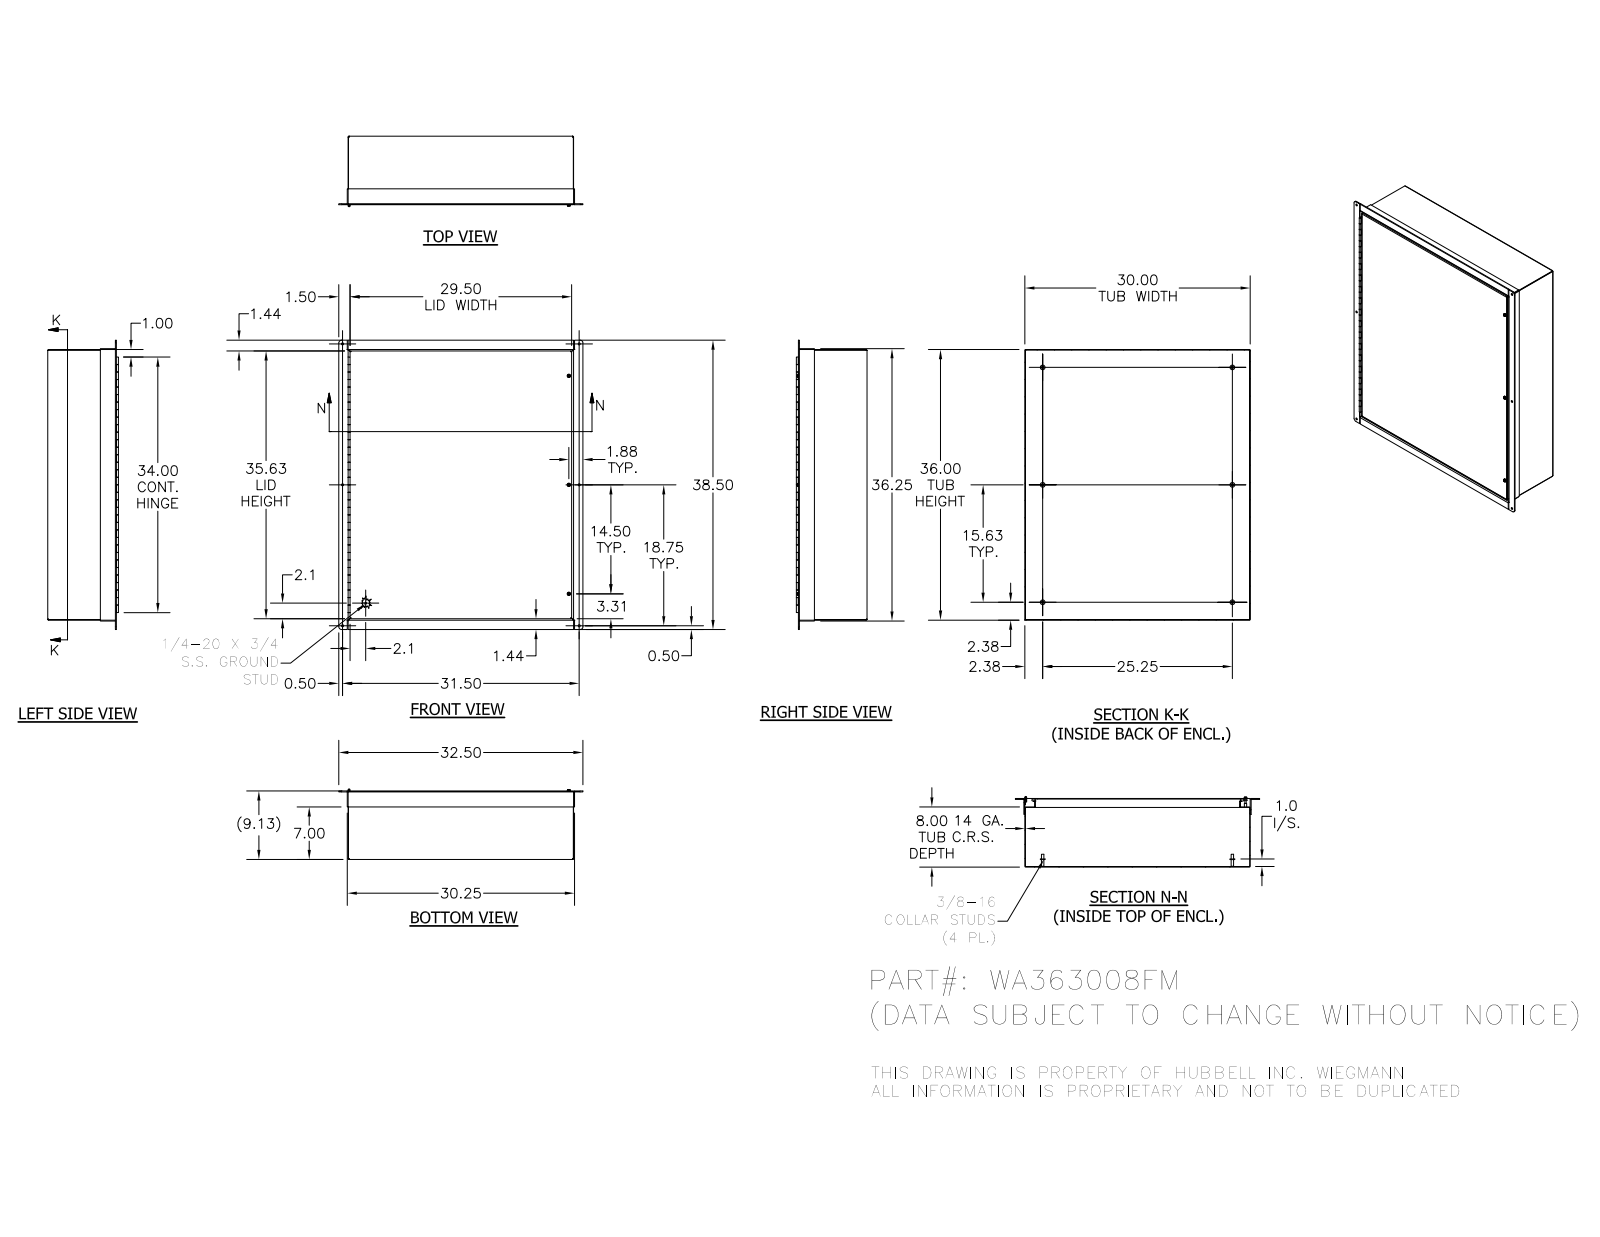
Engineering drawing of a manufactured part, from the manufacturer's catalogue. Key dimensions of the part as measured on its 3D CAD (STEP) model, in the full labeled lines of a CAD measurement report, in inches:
Part name (STEP PRODUCT): WA363008FMBKP; WA3630FMLID; 388116; H6010103T (+8 more)
STEP written by: Autodesk Inventor 2016 (AUTOMOTIVE_DESIGN)
Units: inches
Bodies: 29 solids, 804 faces (508 planar, 215 cylindrical, 81 other)
Overall size (bounding box): 38.5 × 32.5 × 9.4
Volume: 334.4 in³ · Surface area: 8 320 in²
Round holes (diameter × count): ⌀0.281 ×9, ⌀0.375 ×6, ⌀0.156 ×3, ⌀0.188 ×3, ⌀0.278 ×3, ⌀0.125 ×1
Round bosses / shafts (diameter × count): ⌀0.625 ×6, ⌀0.33 ×6, ⌀0.453 ×3, ⌀0.437 ×3, ⌀0.414 ×3, ⌀0.313 ×3, ⌀0.19 ×3, ⌀0.031 ×3
Partial cylindrical surfaces — rounded edges, fillets, slot ends (radius × count): R0.031 ×24, R0.105 ×20, R0.07 ×8, R0.125 ×8, R0.156 ×4, R0.375 ×4, R0.089 ×3
Main face-to-face distances: 0.074, 9.041, 8.967, 9.115, 29.926, 35.926, 0.125, 30, 7.926, 1.115
Hole centre spacings: 18.75, 36.658, 4.467, 6, 14.5, 14.565, 31.5, 33.278
